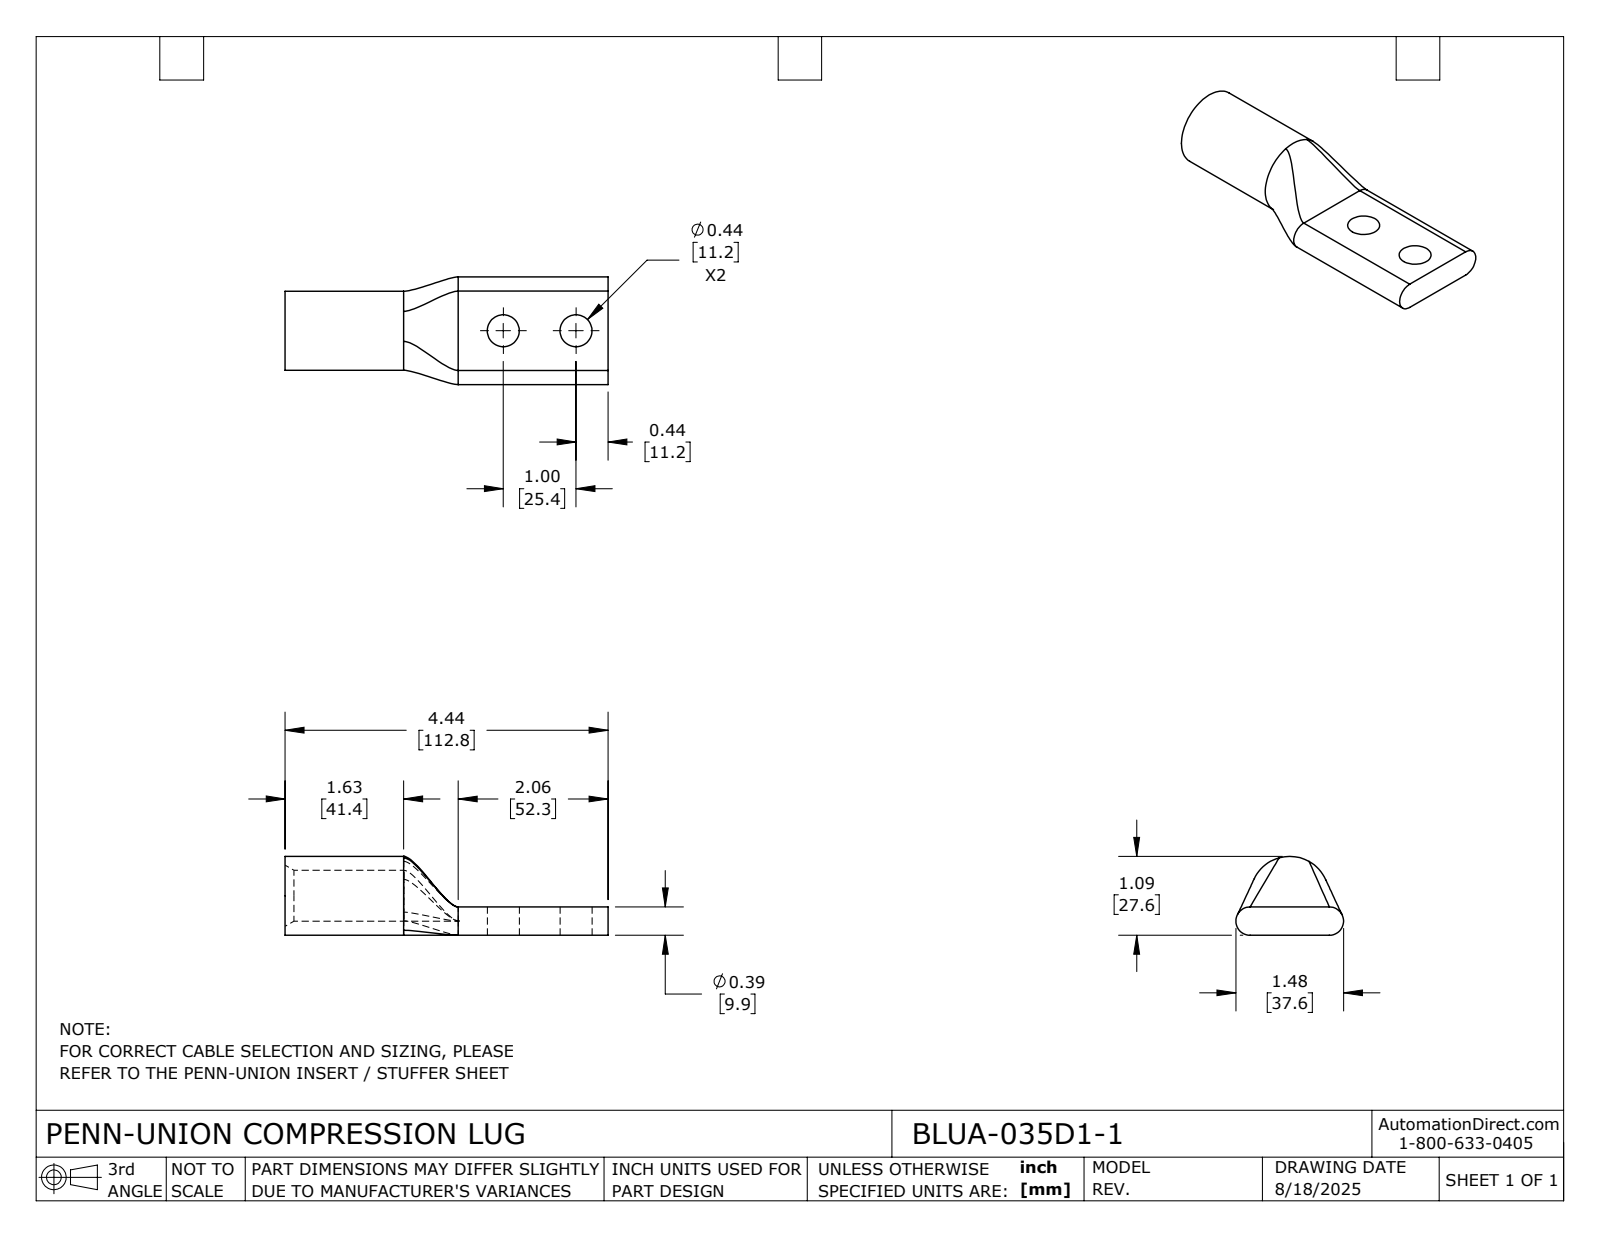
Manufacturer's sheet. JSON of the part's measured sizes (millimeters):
{"part_name": "BLUA-035D1-1", "step_written_by": "SolidWorks 2024 (CONFIG_CONTROL_DESIGN)", "units": "millimeters", "bodies": {"solids": 1, "faces": 26, "planar": 5, "cylindrical": 11, "other": 10}, "overall_size": [112.8, 37.6, 27.6], "volume_mm3": 37310, "surface_area_mm2": 14370, "round_holes": [[11.2, 2], [17.8, 1]], "round_bosses_or_shafts": [[27.6, 1]], "partial_cylinders_radius": [[5, 2]], "face_to_face_distances": [9.9, 112.8, 60.5, 52.3], "hole_center_spacings": [25.4]}
